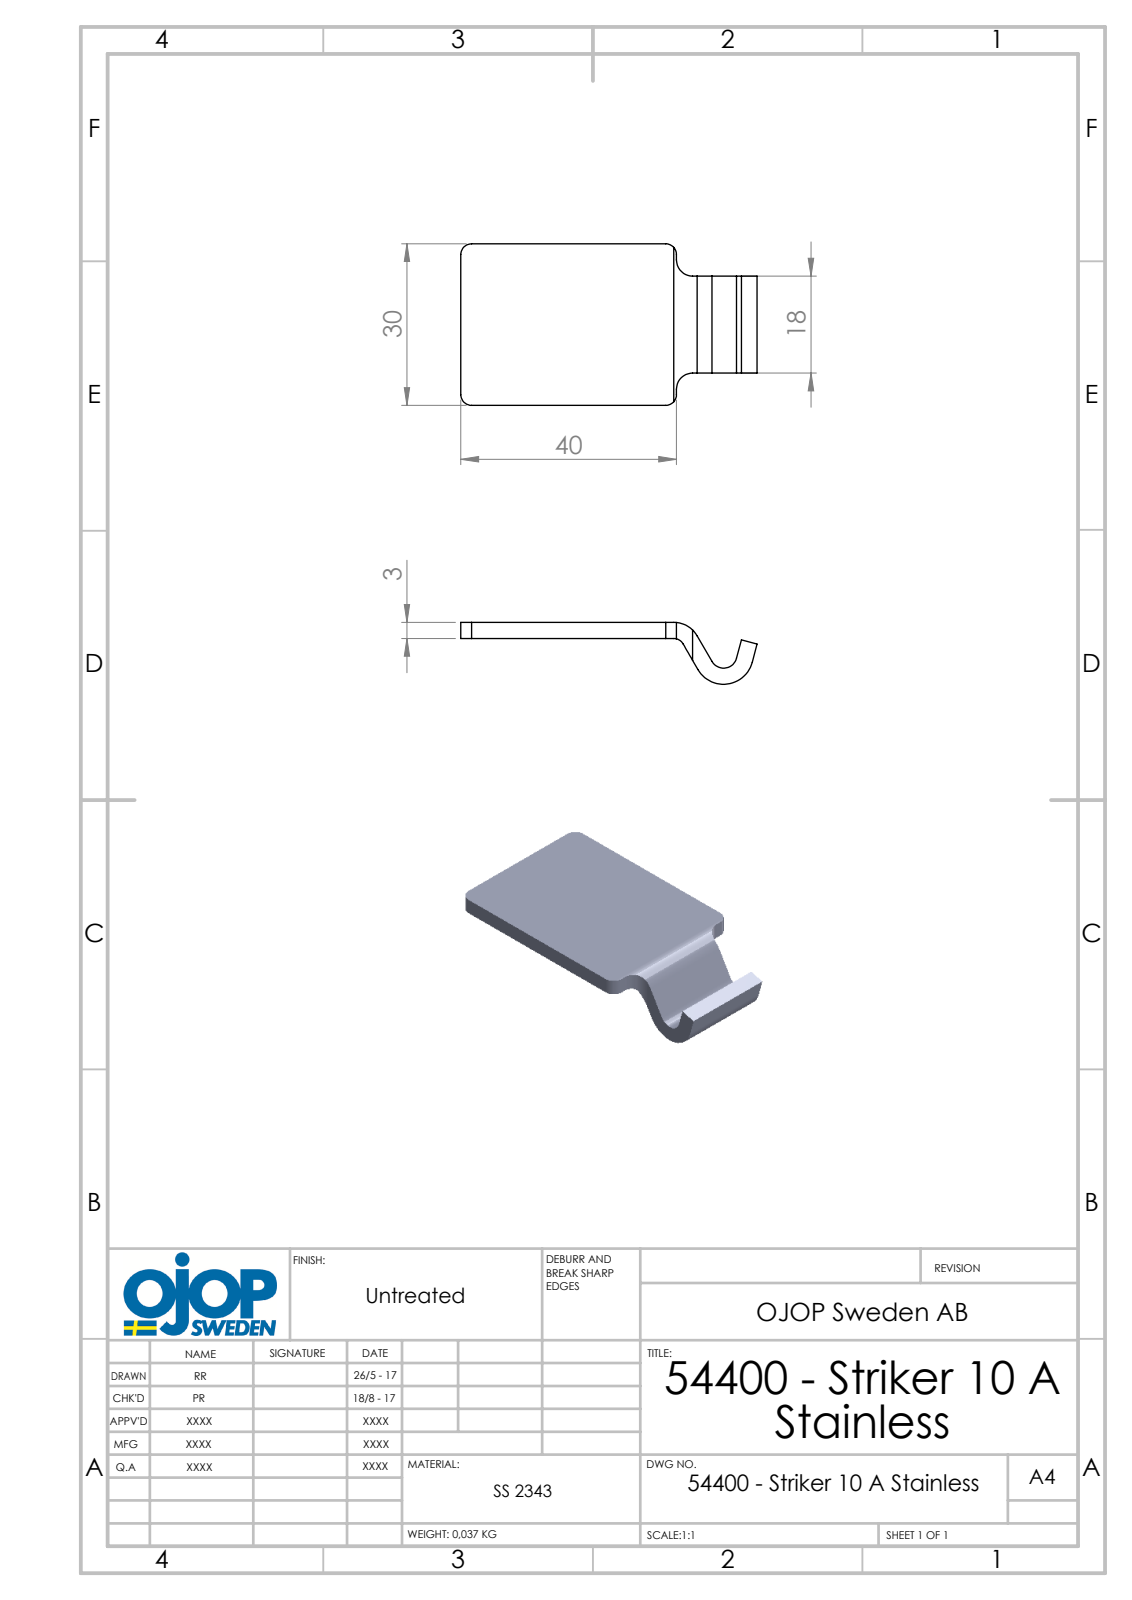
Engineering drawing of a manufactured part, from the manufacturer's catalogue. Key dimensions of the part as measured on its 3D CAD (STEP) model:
Part name (STEP PRODUCT): 54400 - Striker 10 A Stainless
STEP written by: SolidWorks 2015 (AUTOMOTIVE_DESIGN)
Units: millimetres
Bodies: 1 solid, 24 faces (14 planar, 10 cylindrical, 0 other)
Overall size (bounding box): 55.53 × 30 × 14.5
Volume: 4 832 mm³ · Surface area: 3 767 mm²
Partial cylindrical surfaces — rounded edges, fillets, slot ends (radius × count): R2 ×5, R3 ×2, R2.5 ×1, R5 ×1, R5.5 ×1
Main face-to-face distances: 3, 6, 24, 30, 18, 38.35
